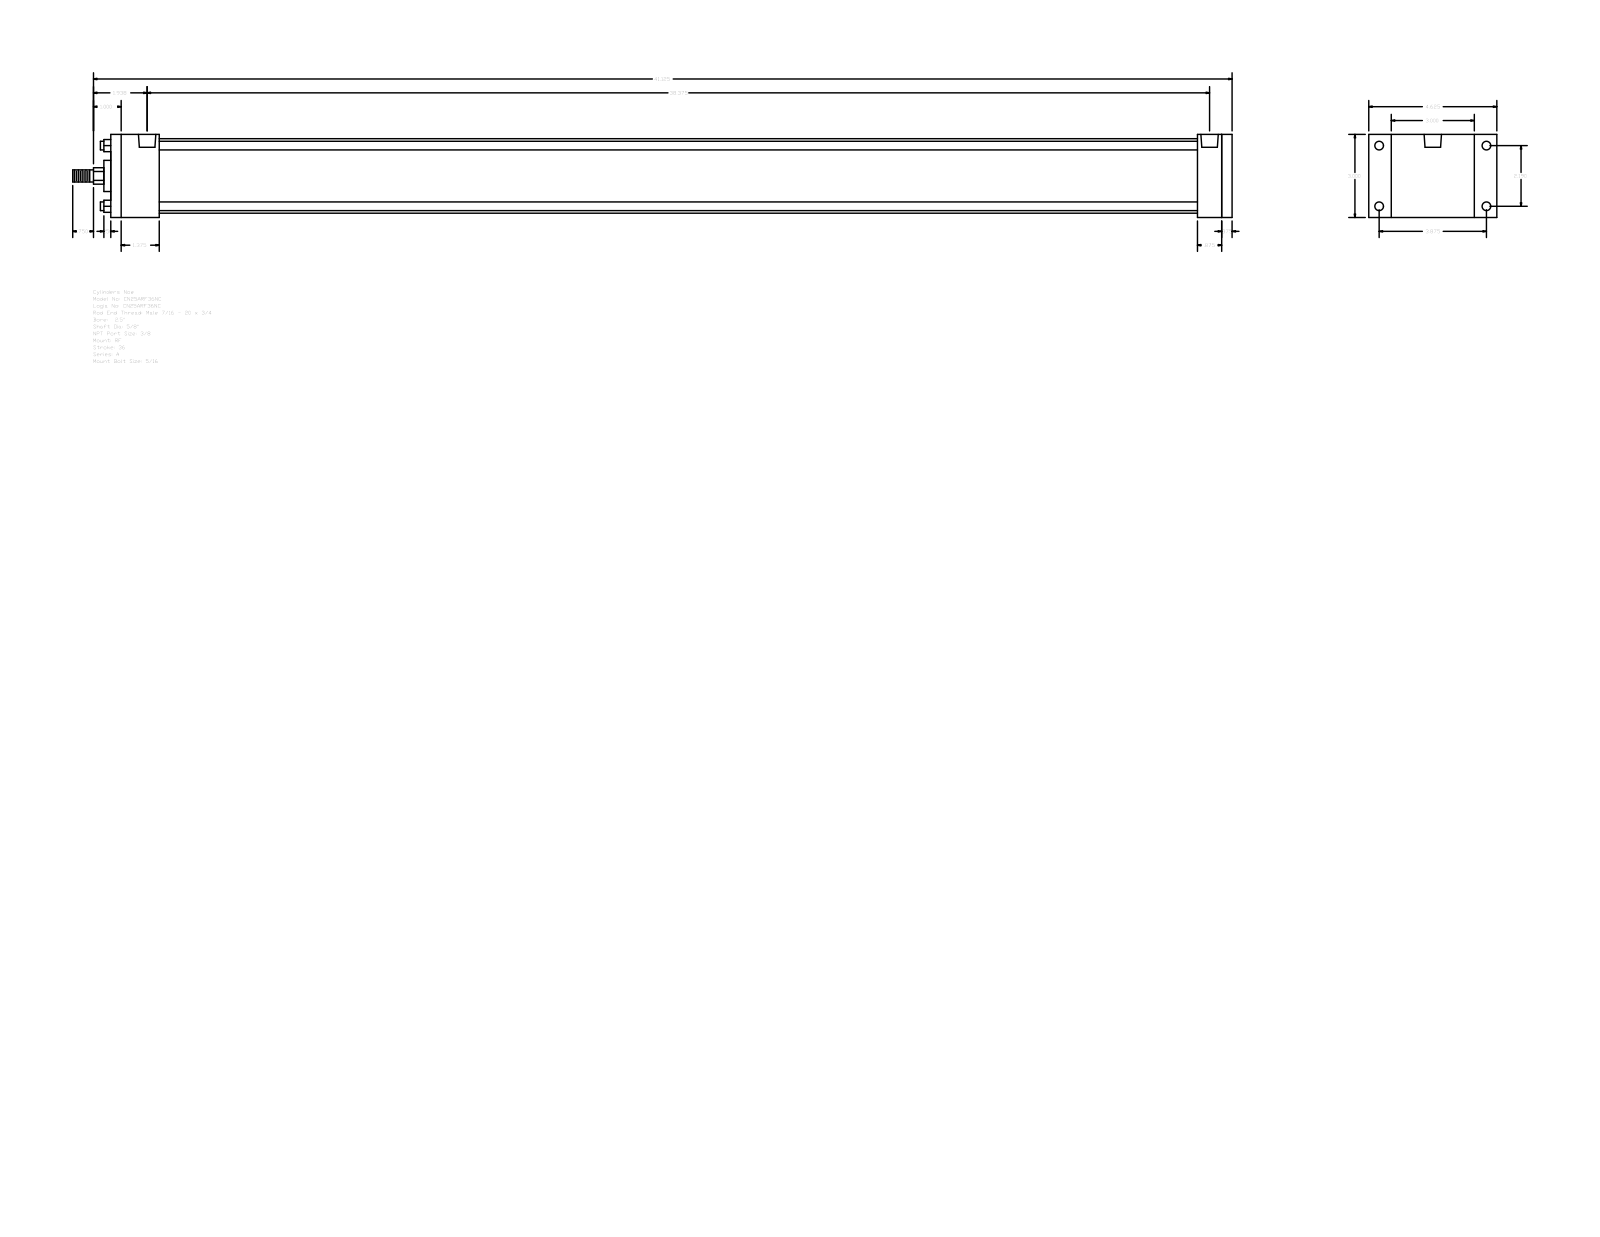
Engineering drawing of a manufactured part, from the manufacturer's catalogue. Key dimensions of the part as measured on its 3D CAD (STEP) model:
Part name (STEP PRODUCT): A_RF__0250_0.625
STEP written by: GSSL Pune (CONFIG_CONTROL_DESIGN)
Units: millimetres
Bodies: 0 solids, 92 faces (64 planar, 28 cylindrical, 0 other)
Overall size (bounding box): 1063.62 × 117.47 × 76.2
Round holes (diameter × count): ⌀5.56 ×4, ⌀7.94 ×4, ⌀15.93 ×2
Round bosses / shafts (diameter × count): ⌀7.94 ×4, ⌀68.33 ×1, ⌀28.57 ×1, ⌀15.88 ×1, ⌀11.11 ×1
Partial cylindrical surfaces — rounded edges, fillets, slot ends (radius × count): R7.54 ×1
Main face-to-face distances: 76.2, 1028.7, 9.53, 1019.17, 44.45, 31.75, 996.95, 952.5, 974.72, 984.25
Hole centre spacings: 2.38, 55.62, 98.42, 113.05, 977.11, 979.49, 974.73
